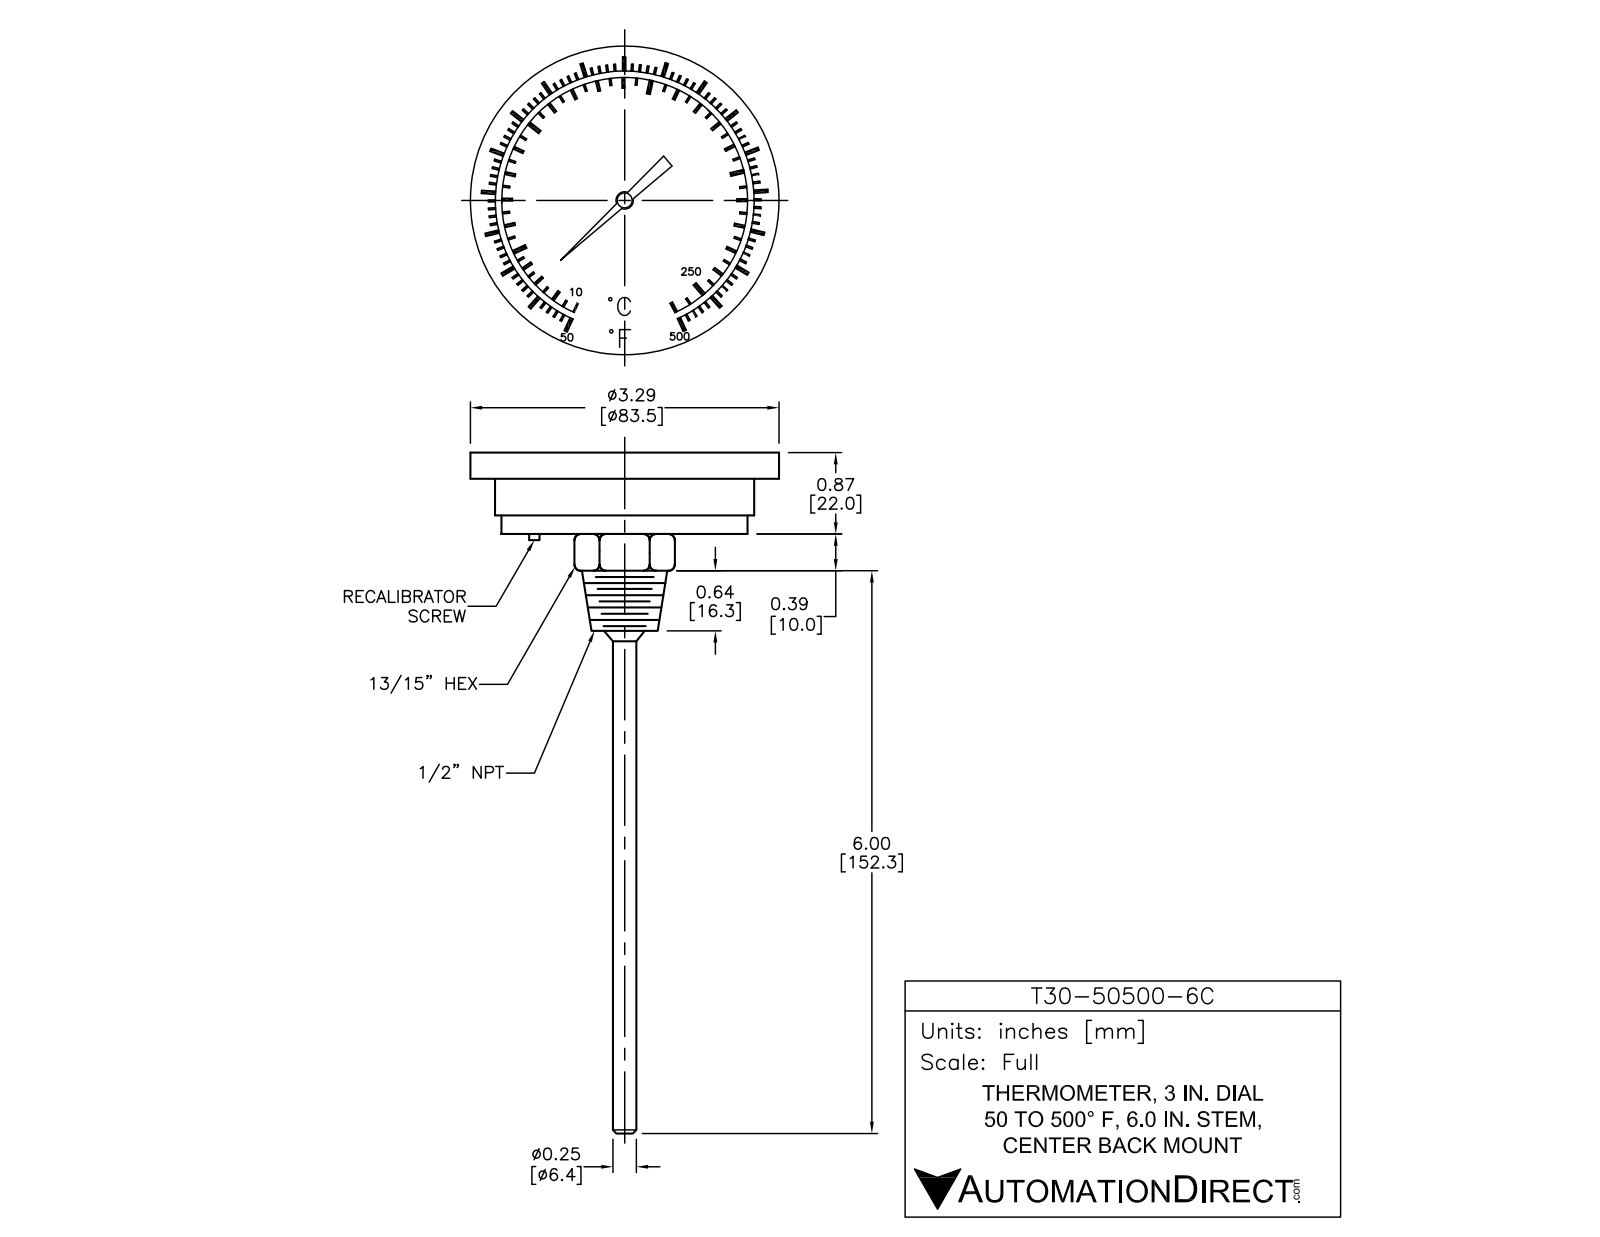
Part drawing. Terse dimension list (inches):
name: T30-50500-6C
written by: SolidWorks 2021 (AUTOMOTIVE_DESIGN)
unit: in
bodies: 57 solids, 934 faces (720 planar, 124 cylindrical, 90 other)
size: 5.26 × 3.29 × 3.29
volume: 3.15 in³; area: 34.08 in²
holes: 1× ⌀0.067, 1× ⌀2.69
bosses: 1× ⌀3.29, 1× ⌀2.76, 1× ⌀2.62, 1× ⌀0.845, 1× ⌀0.258
rounds: 1× R0.04, 1× R0.859, 1× R0.969
face distances: 0.222, 0.078, 0.3, 0.87, 0.648, 0.57, 0.29, 0.59, 0.368, 0.28
